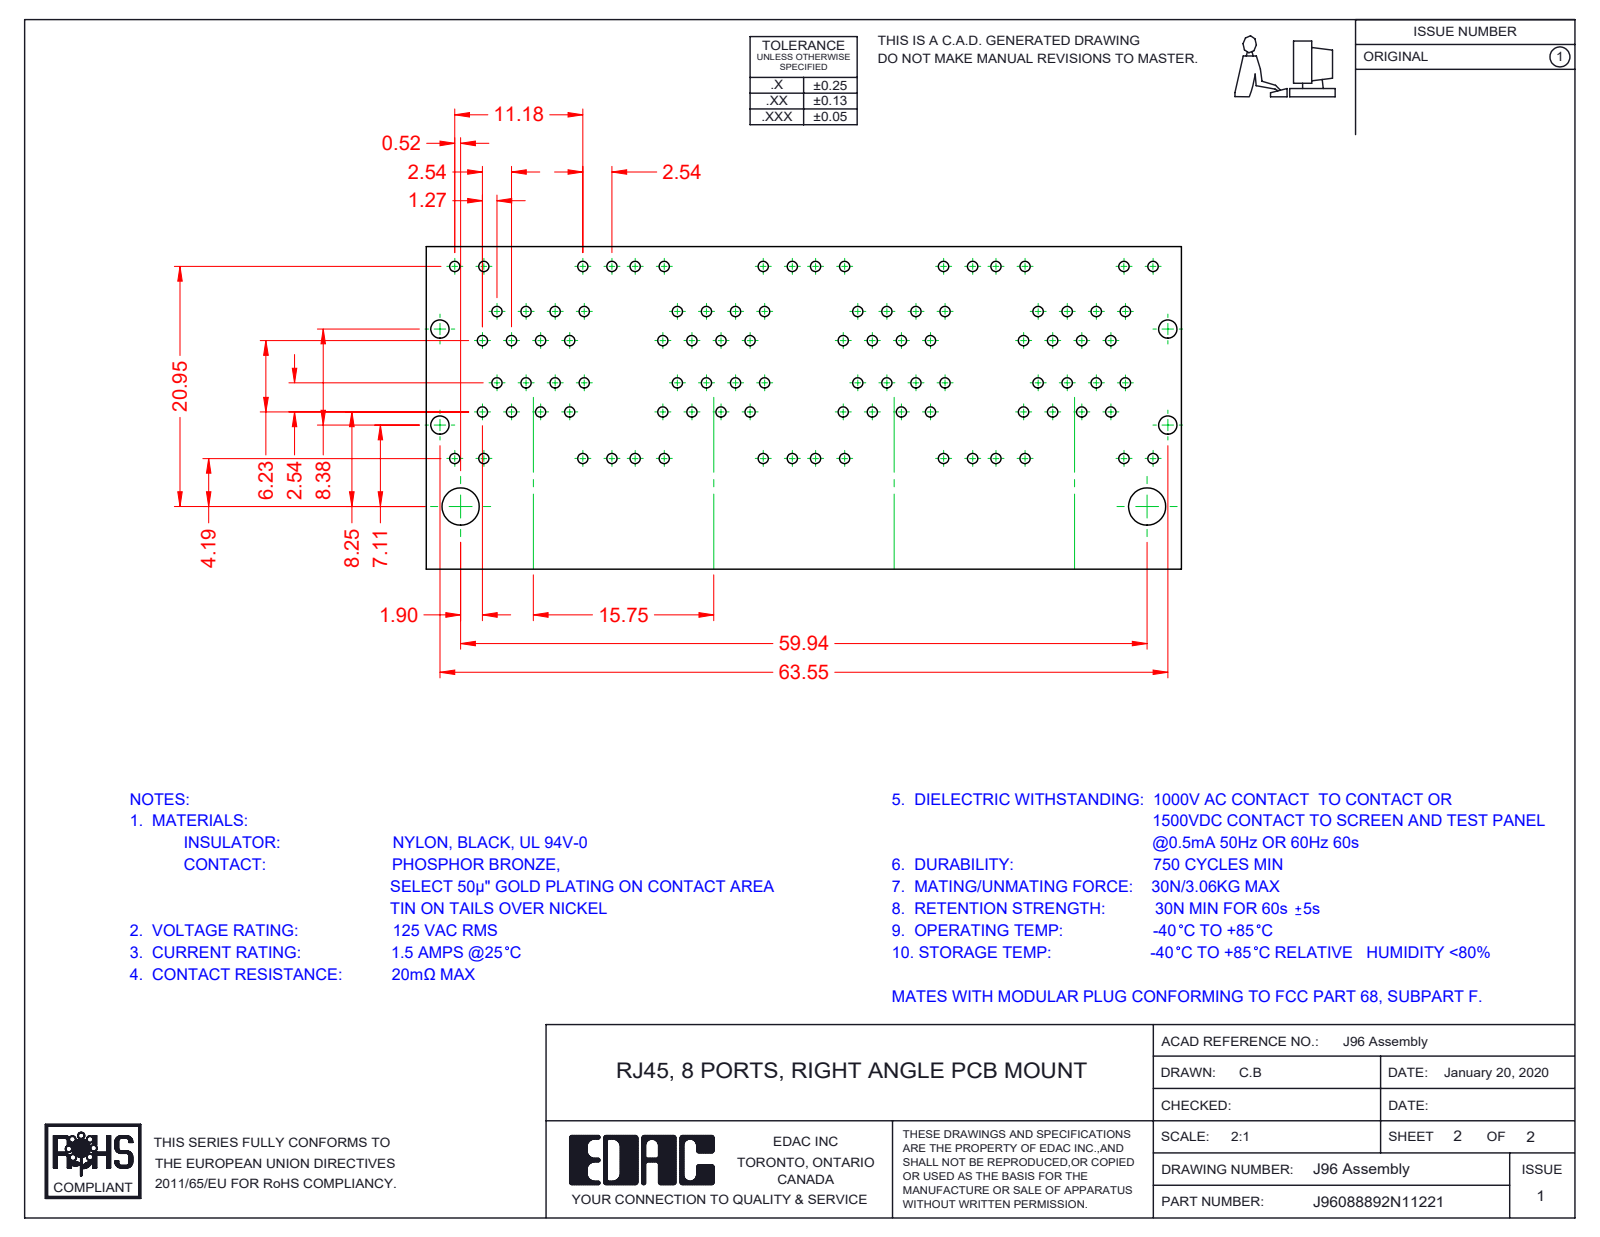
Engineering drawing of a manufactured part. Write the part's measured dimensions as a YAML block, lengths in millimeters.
part_name: "96 Contacts Upper; 96 Insulator Insert; 96 Shield_8 Ports LED - EMI; J96088892N11221 (+8 more)"
step_written_by: "SolidWorks 2016 (CONFIG_CONTROL_DESIGN)"
units: millimeters
bodies: {solids: 96, faces: 7804, planar: 6105, cylindrical: 1388, other: 311}
overall_size: [67.35, 31.38, 28.68]
volume: 24149
surface_area: 63596
round_holes:
  - {diameter: 1.7, count: 3}
round_bosses_or_shafts:
  - {diameter: 1.68, count: 3}
partial_cylinders:
  - {radius: 0.25, count: 124}
  - {radius: 0.35, count: 73}
  - {radius: 1, count: 72}
  - {radius: 0.5, count: 49}
  - {radius: 0.91, count: 32}
  - {radius: 0.2, count: 27}
  - {radius: 0.27, count: 14}
  - {radius: 0.7, count: 11}
face_to_face_distances: [15.75, 0.35, 9.95, 1.17, 1.6, 0.54, 9.98, 10.18, 12.67, 3.37]
hole_center_spacings: [15.75, 31.5]
